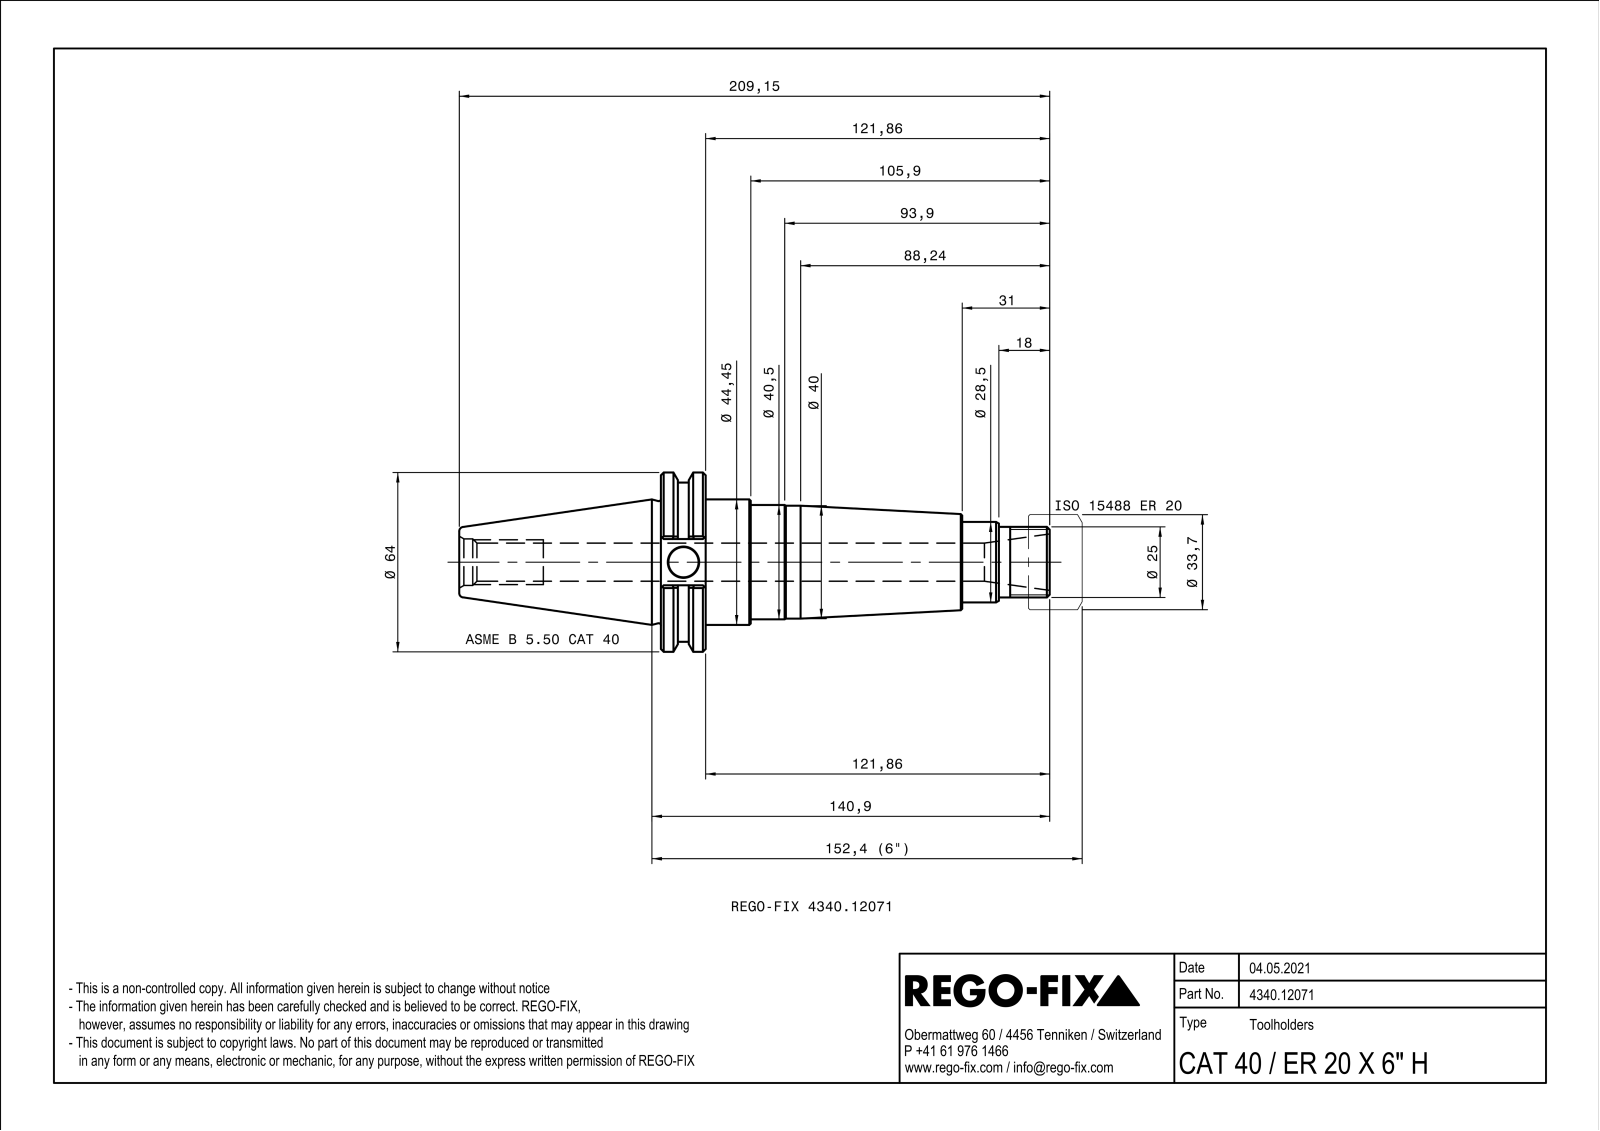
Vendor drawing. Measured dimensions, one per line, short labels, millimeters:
name: NOCUT
written by: SIEMENS PLM Software Solid Edge ST10 (AUTOMOTIVE_DESIGN)
unit: mm
bodies: 1 solid, 118 faces (33 planar, 26 cylindrical, 59 other)
size: 209.15 × 63.5 × 60.79
volume: 206 236 mm³; area: 38 659 mm²
holes: 1× ⌀10.7, 1× ⌀13.5, 1× ⌀13.53, 1× ⌀16.5
bosses: 1× ⌀63.5, 1× ⌀56.36, 1× ⌀44.45, 1× ⌀40.5, 1× ⌀40, 1× ⌀28.5, 1× ⌀25
rounds: 4× R0.5
face distances: 15.87, 90.86, 106.73, 47.33, 16.38, 74.9, 15.96, 31.83, 178.15, 103.25
